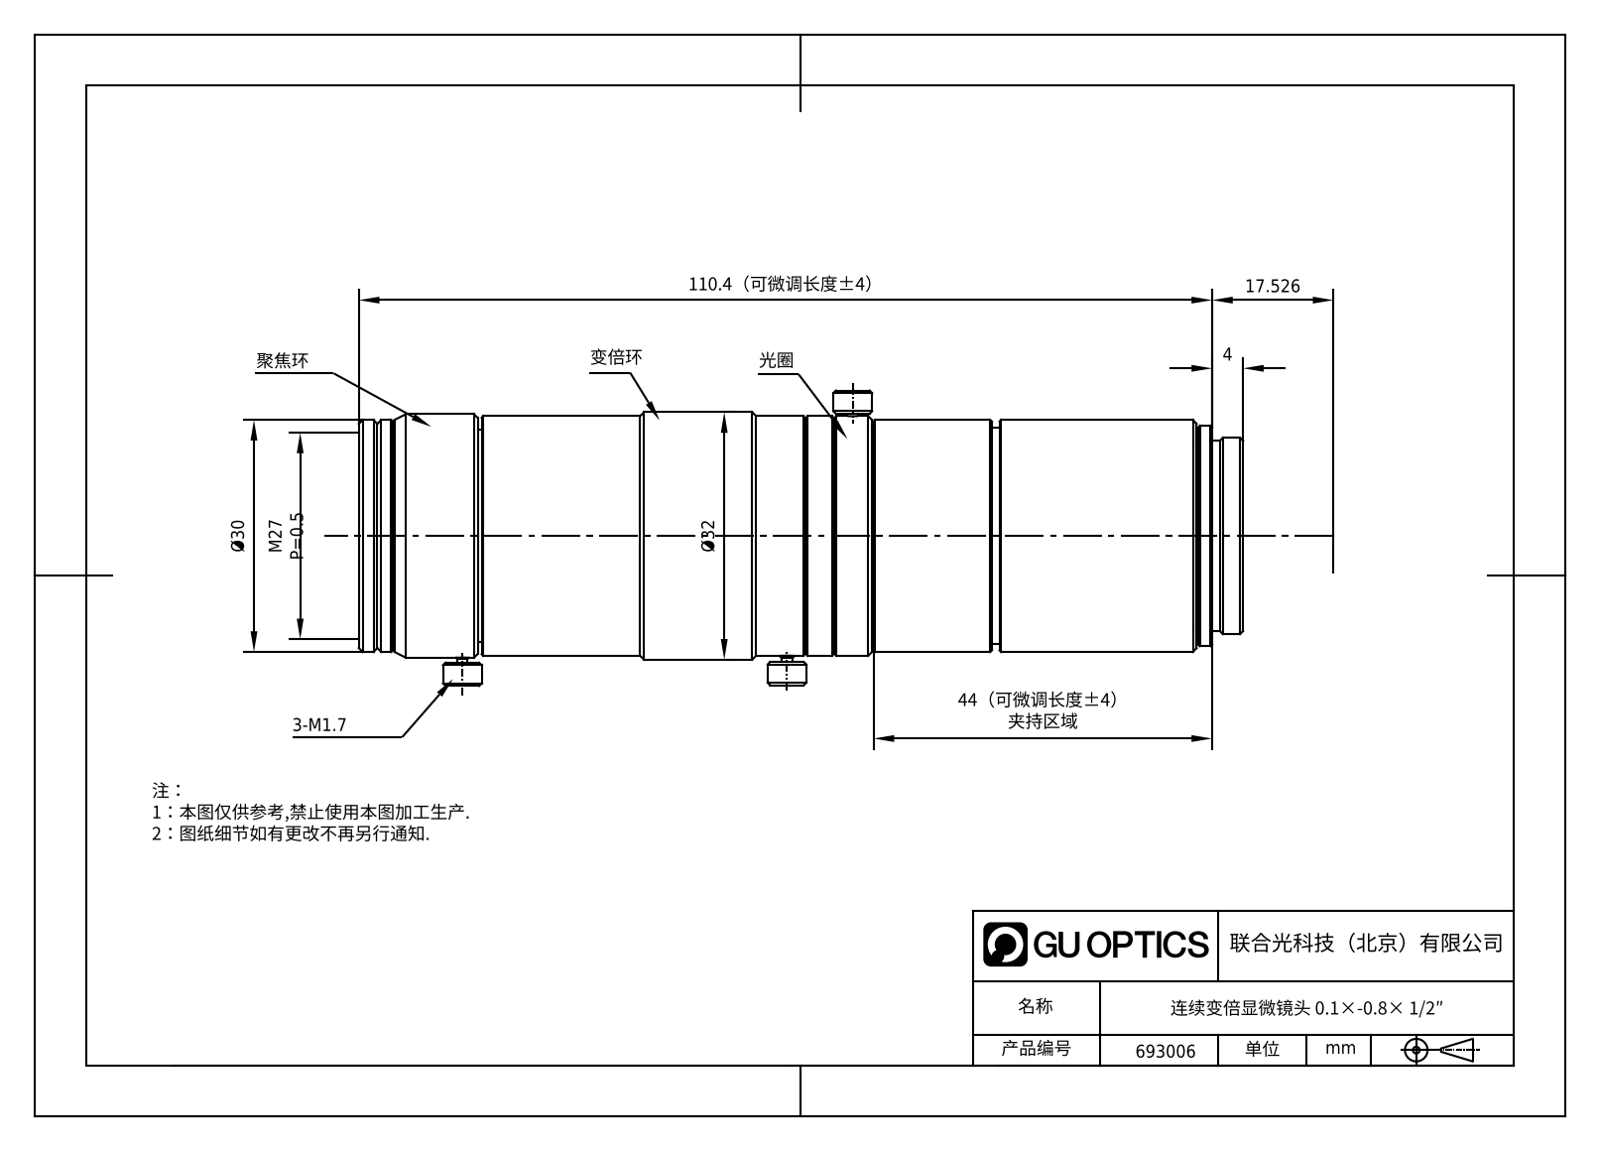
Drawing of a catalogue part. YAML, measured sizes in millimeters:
part_name: "Z0108N"
step_written_by: "SolidWorks 2020 (CONFIG_CONTROL_DESIGN)"
units: millimeters
bodies: {solids: 1, faces: 170, planar: 28, cylindrical: 66, other: 76}
overall_size: [114.4, 38.2, 32]
volume: 78387
surface_area: 15305
round_holes:
  - {diameter: 17, count: 1}
  - {diameter: 19.5, count: 1}
  - {diameter: 21.5, count: 1}
  - {diameter: 26.5, count: 1}
  - {diameter: 27, count: 1}
round_bosses_or_shafts:
  - {diameter: 5, count: 3}
  - {diameter: 1.35, count: 3}
  - {diameter: 32, count: 1}
  - {diameter: 31.5, count: 1}
  - {diameter: 31, count: 1}
  - {diameter: 30, count: 1}
  - {diameter: 29, count: 1}
  - {diameter: 28.5, count: 1}
face_to_face_distances: [94.5, 0.5, 47, 42, 50.7, 8.5, 6.5, 50.5, 44, 5]
